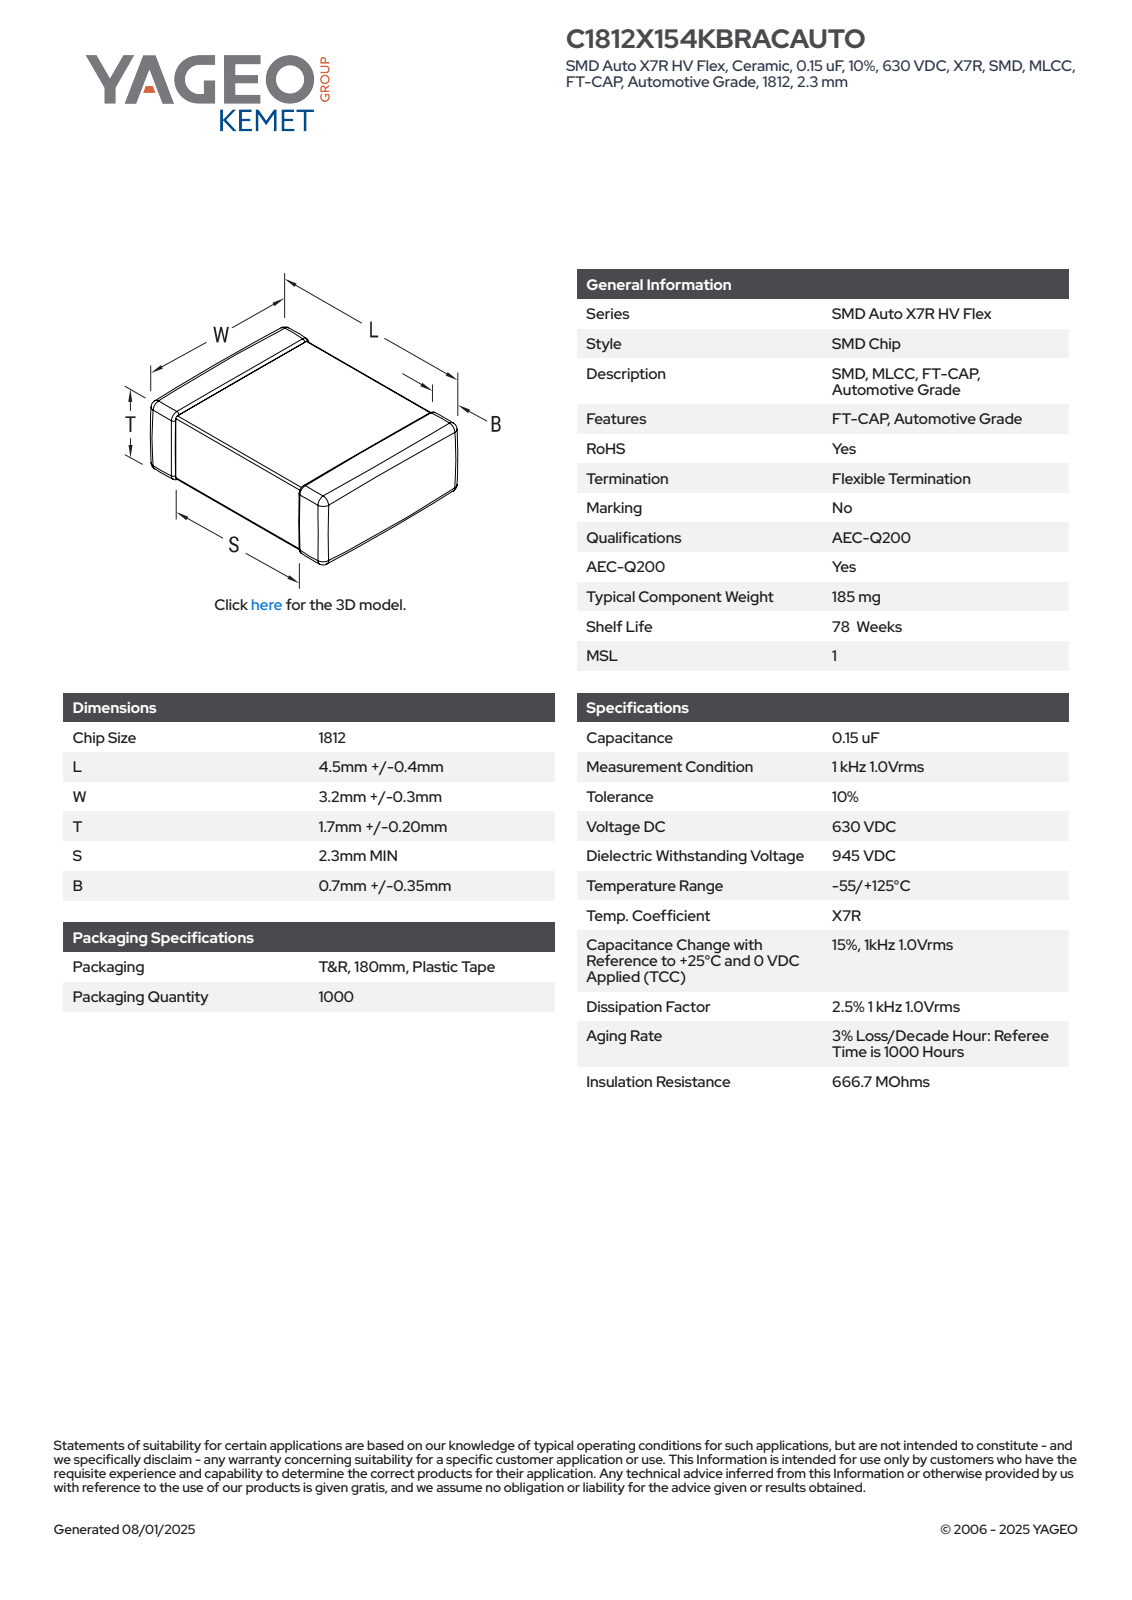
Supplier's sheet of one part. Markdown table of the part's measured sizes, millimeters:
| quantity | value |
| --- | --- |
| part name | CCS_CCSTD_1812_L4.9W3.5T1.9B0.7 |
| STEP written by | SolidWorks 2021 (AUTOMOTIVE_DESIGN) |
| units | millimeters |
| bodies | 4 solids, 121 faces (71 planar, 34 cylindrical, 16 other) |
| overall size | 4.9 × 3.5 × 1.9 |
| volume | 30 mm³ |
| surface area | 66 mm² |
| main face-to-face distances | 1.83, 1.76, 3.43, 1.9, 4.9, 3.36, 3.5, 0.52, 2.25, 2.13 |
